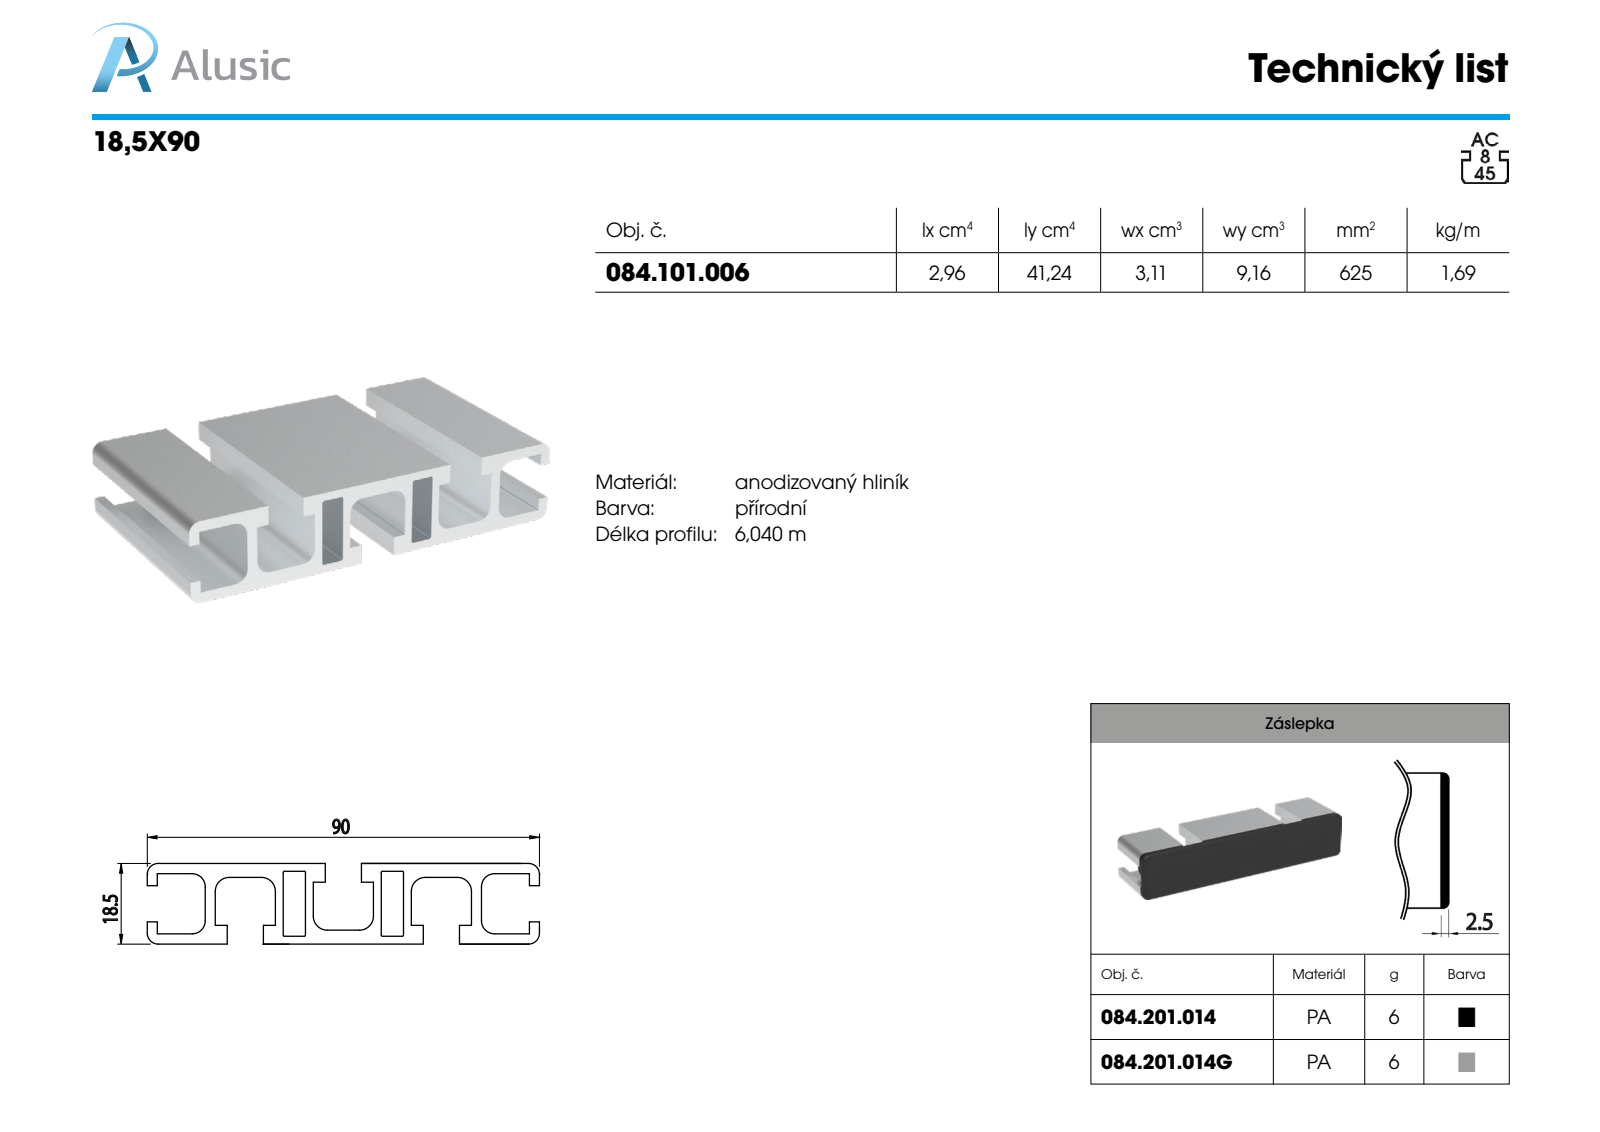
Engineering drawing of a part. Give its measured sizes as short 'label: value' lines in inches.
name: 084.101.006
written by: SolidWorks 2018 (AUTOMOTIVE_DESIGN)
unit: in
bodies: 1 solid, 76 faces (54 planar, 22 cylindrical, 0 other)
size: 3.937 × 3.543 × 0.728
volume: 3.803 in³; area: 76.04 in²
rounds: 10× R0.118, 8× R0.02, 4× R0.098
face distances: 0.728, 0.886, 0.071, 0.614, 0.543, 0.201, 0.815, 0.272, 0.093, 0.636
